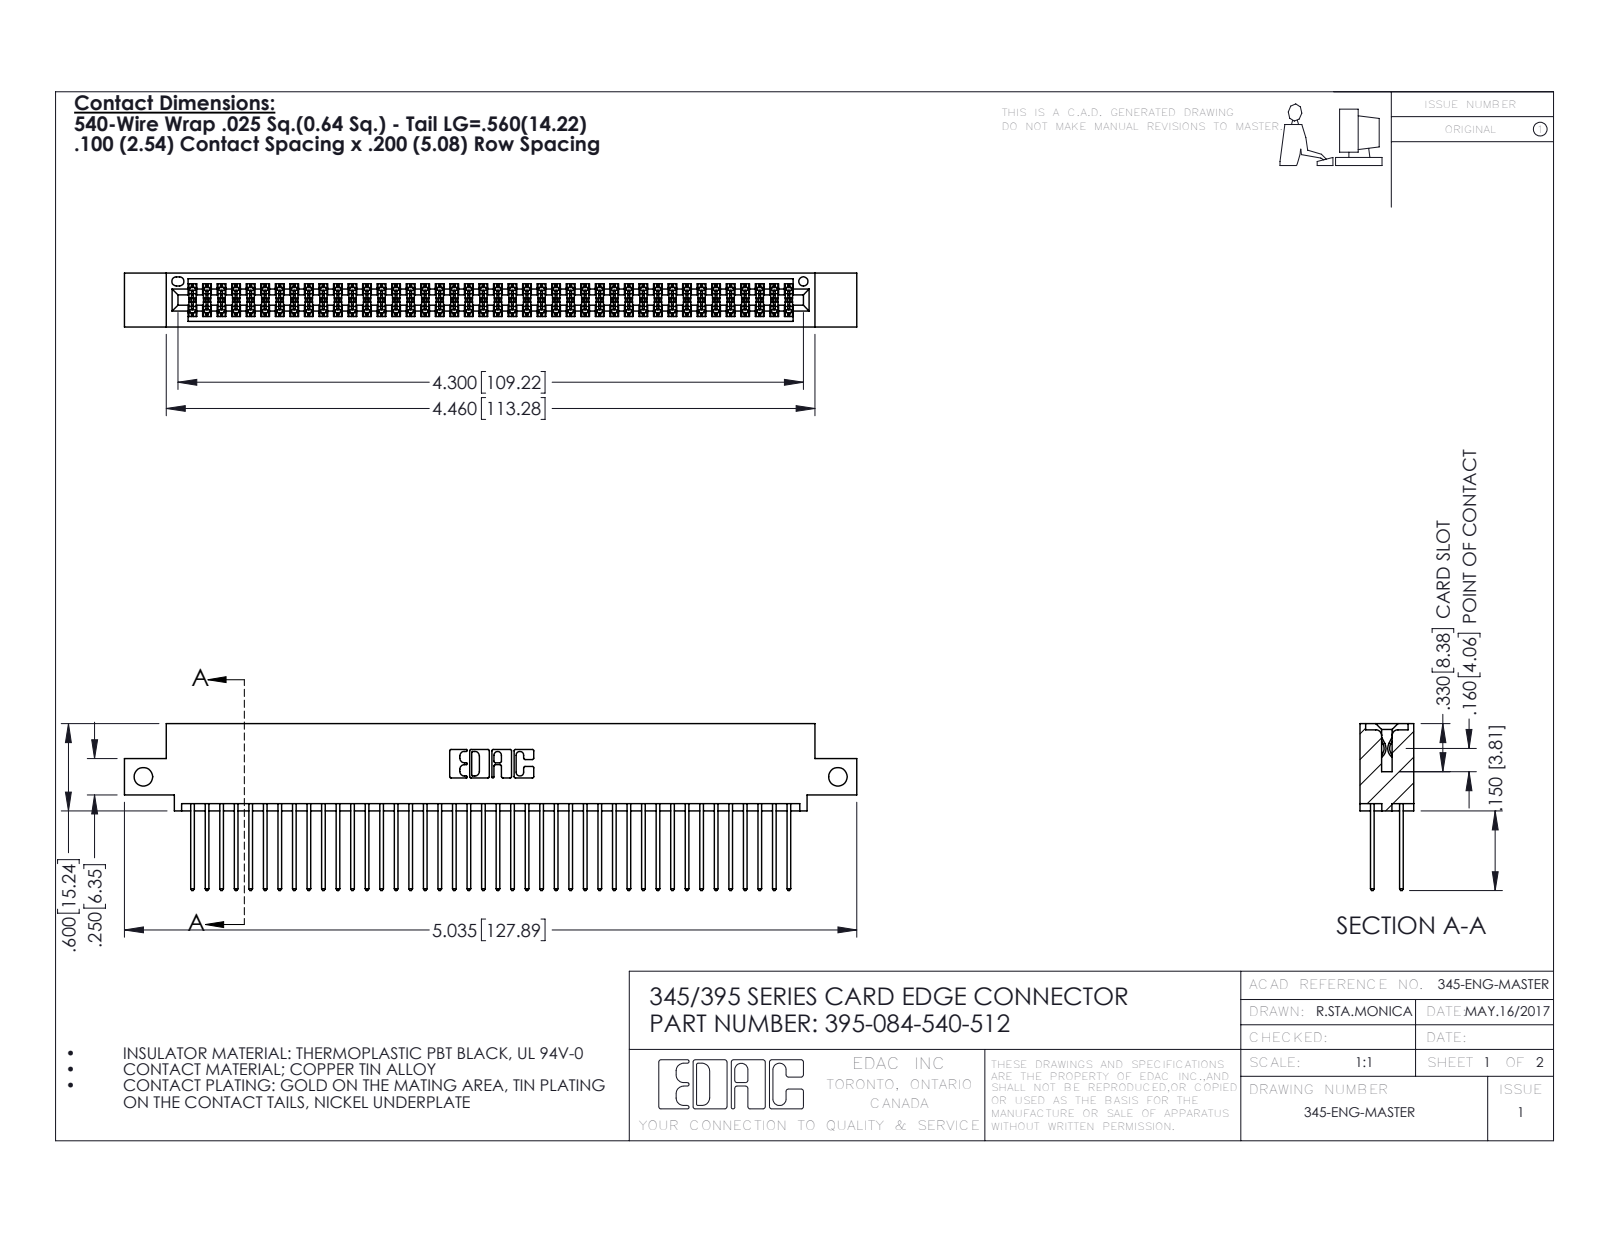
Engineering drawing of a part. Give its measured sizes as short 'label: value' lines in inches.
name: 345-292-001_345-293-140; 395-084-540-512; 345 Part_0.110 Offset - Side Mount
written by: SolidWorks 2016 (CONFIG_CONTROL_DESIGN)
unit: in
bodies: 85 solids, 4330 faces (2856 planar, 1474 cylindrical, 0 other)
size: 5.035 × 1.147 × 0.37
volume: 0.768 in³; area: 31.05 in²
holes: 2× ⌀0.128, 1× ⌀0.064
rounds: 126× R0.006, 84× R0.01, 22× R0.01, 6× R0.007, 6× R0.031, 3× R0.026, 2× R0.014, 2× R0.019
face distances: 0.298, 0.072, 0.2, 0.098, 0.272, 0.025, 0.37, 0.225, 0.175, 0.149
hole spacings: 4.775
